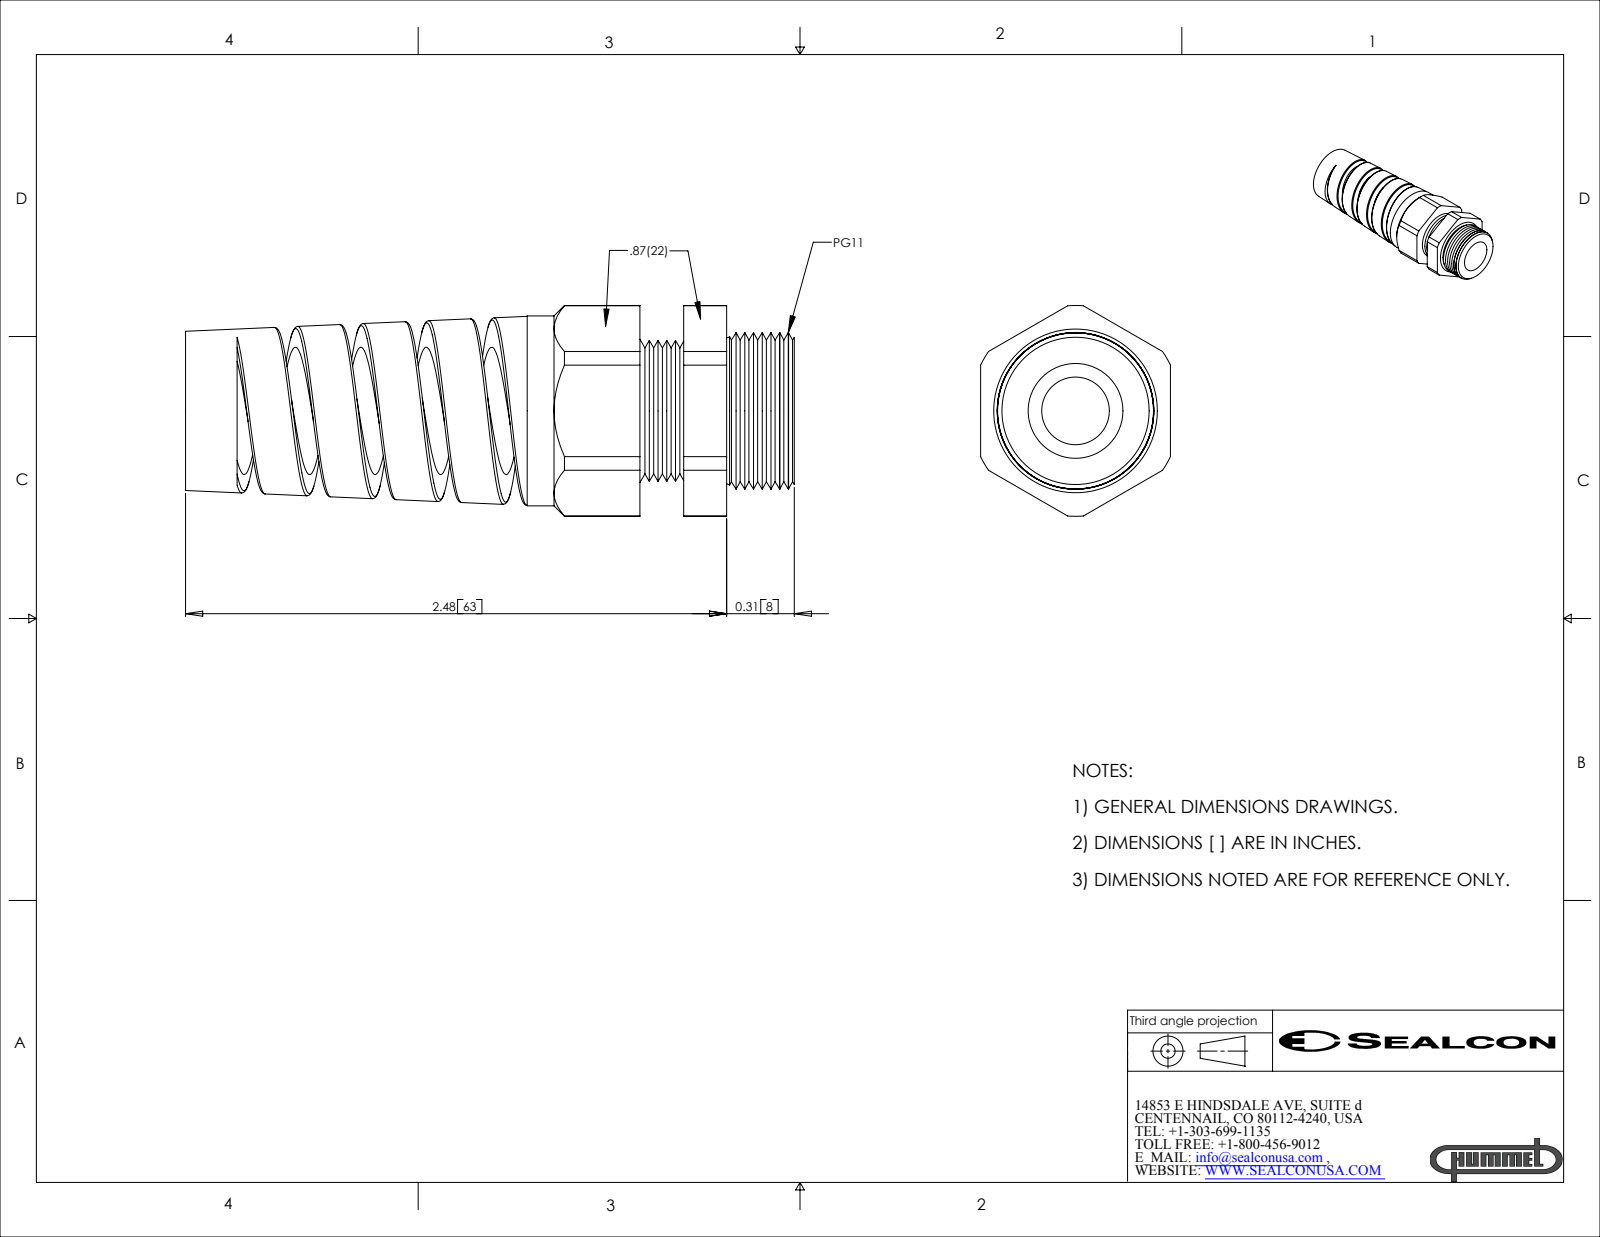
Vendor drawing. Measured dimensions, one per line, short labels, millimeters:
name: CF11BA-BK
written by: SolidWorks 2007 (CONFIG_CONTROL_DESIGN)
unit: mm
bodies: 2 solids, 146 faces (24 planar, 35 cylindrical, 87 other)
size: 70.9 × 24.5 × 22.1
volume: 12 700 mm³; area: 10 610 mm²
holes: 1× ⌀7.9, 1× ⌀14.8, 1× ⌀16.7
bosses: 1× ⌀22.1
rounds: 1× R7.7, 1× R12.3
face distances: 22.1, 5.1, 10.1, 5, 18, 12.9, 7.9, 11.3, 16.3, 21.3
